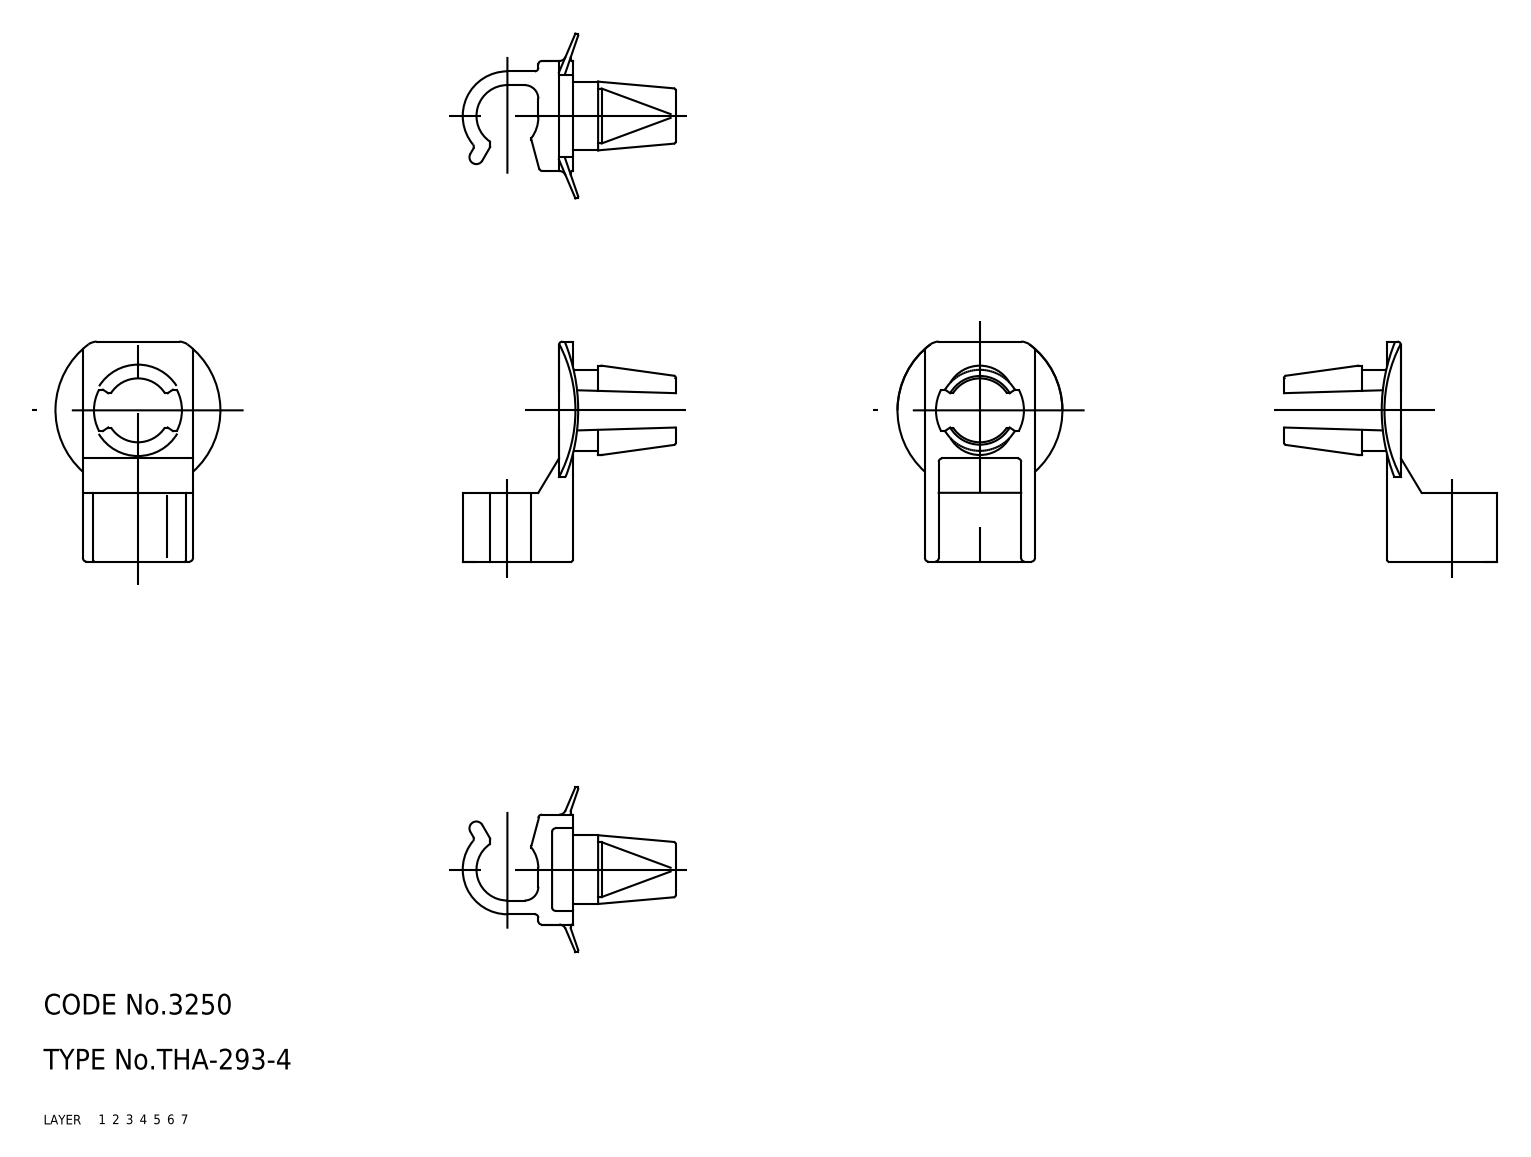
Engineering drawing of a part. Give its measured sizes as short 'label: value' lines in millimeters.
name: holder
written by: CADfix (AUTOMOTIVE_DESIGN)
unit: mm
bodies: 1 solid, 98 faces (0 planar, 0 cylindrical, 98 other)
size: 32 × 31 × 24
volume: 1 869 mm³; area: 2 616 mm²
